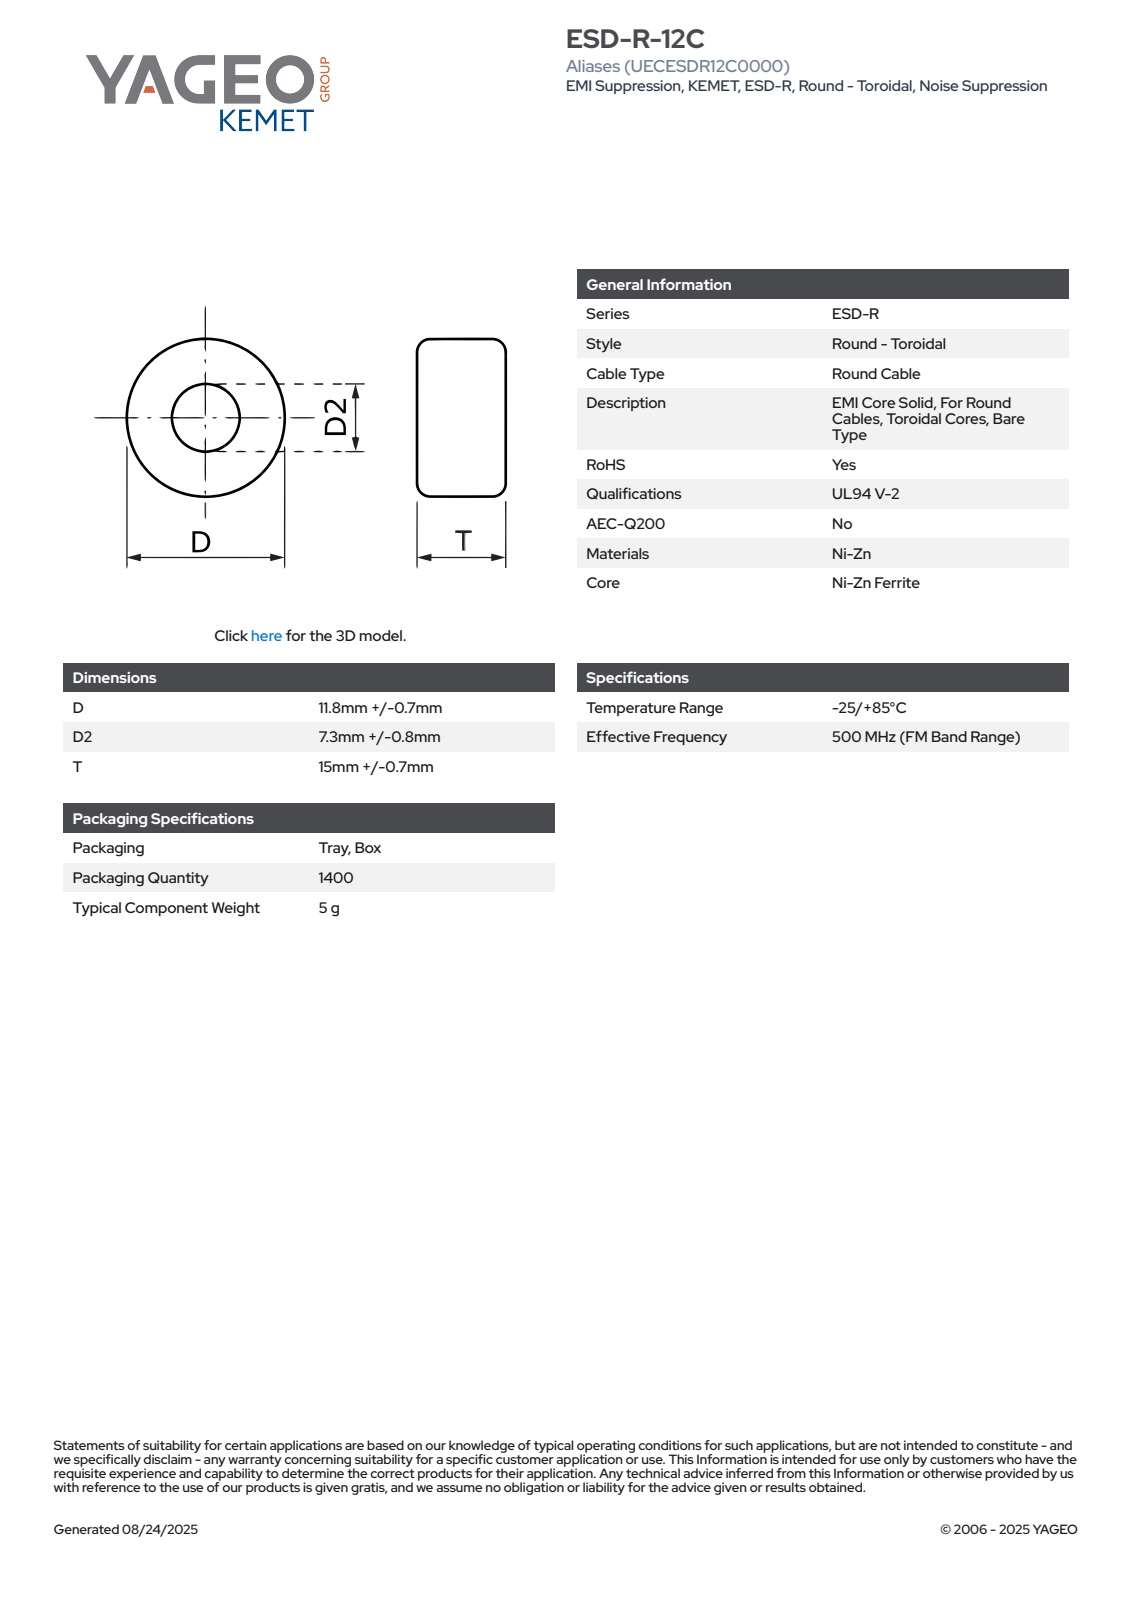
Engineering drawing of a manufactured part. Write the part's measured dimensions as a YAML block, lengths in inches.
part_name: "EC_KBC_D12.5D27.3T15.7"
step_written_by: "SolidWorks 2021 (AUTOMOTIVE_DESIGN)"
units: inches
bodies: {solids: 1, faces: 66, planar: 24, cylindrical: 7, other: 35}
overall_size: [0.618, 0.493, 0.492]
volume: 0.077
surface_area: 1.747
round_holes:
  - {diameter: 0.287, count: 1}
round_bosses_or_shafts:
  - {diameter: 0.492, count: 1}
partial_cylinders:
  - {radius: 0.246, count: 1}
face_to_face_distances: [0.618, 0.276, 0.343, 0.067, 0.013, 0.288, 0.33, 0.054, 0.042, 0.317]
